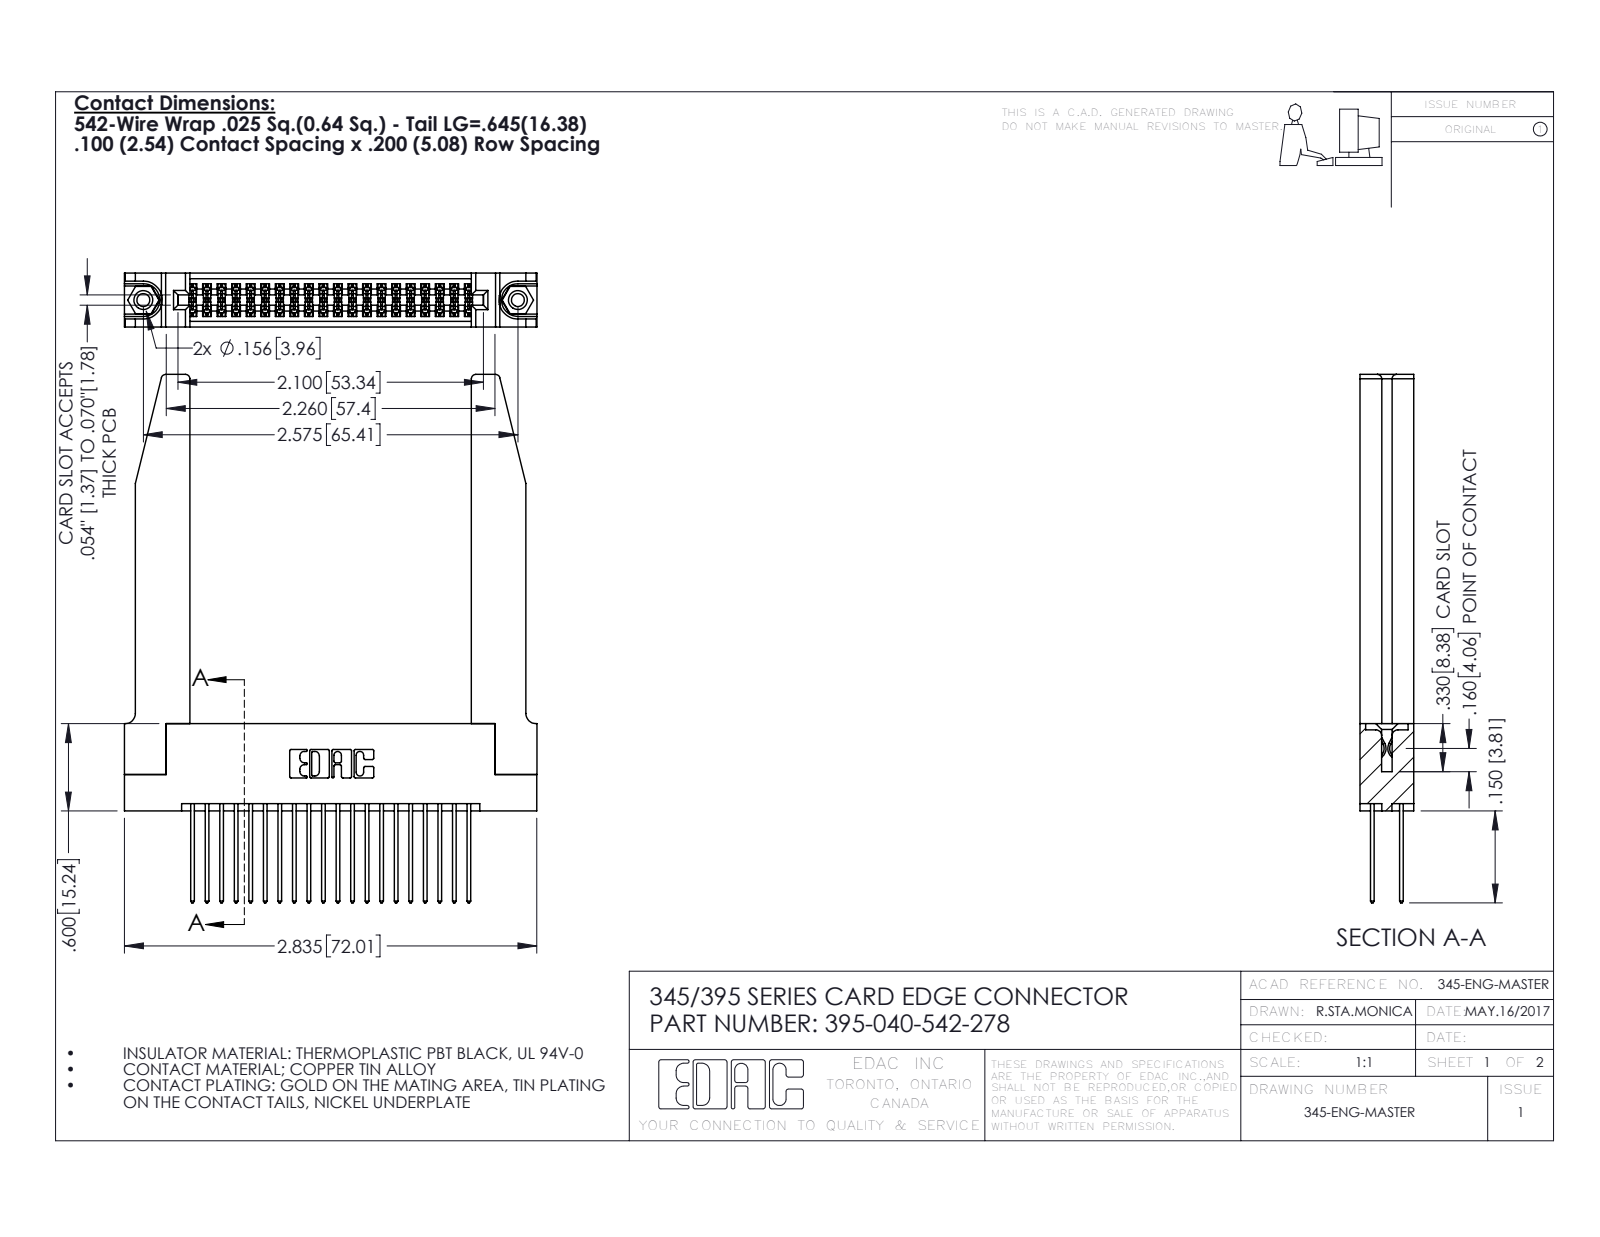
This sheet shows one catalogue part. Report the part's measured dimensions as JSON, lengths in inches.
{"part_name": "395-040-542-278; 345 Part_Flush Mounting Lugs - 0.156 Dia-TH; 345-250-001_345-250-001-102; 345-220-078_345-220-078 (+1 more)", "step_written_by": "SolidWorks 2016 (CONFIG_CONTROL_DESIGN)", "units": "inches", "bodies": {"solids": 45, "faces": 2360, "planar": 1542, "cylindrical": 766, "other": 52}, "overall_size": [3.632, 2.836, 0.37], "volume_in3": 0.9, "surface_area_in2": 27.28, "round_holes": [[0.089, 2], [0.125, 2], [0.156, 2], [0.064, 1]], "round_bosses_or_shafts": [[0.155, 2]], "partial_cylinders_radius": [[0.006, 60], [0.01, 40], [0.01, 22], [0.03, 8], [0.007, 6], [0.031, 6], [0.026, 3], [0.014, 2]], "face_to_face_distances": [0.37, 0.072, 0.298, 0.2, 0.098, 0.272, 0.025, 0.225, 0.148, 0.15], "hole_center_spacings": [0.27, 2.341, 2.575]}
